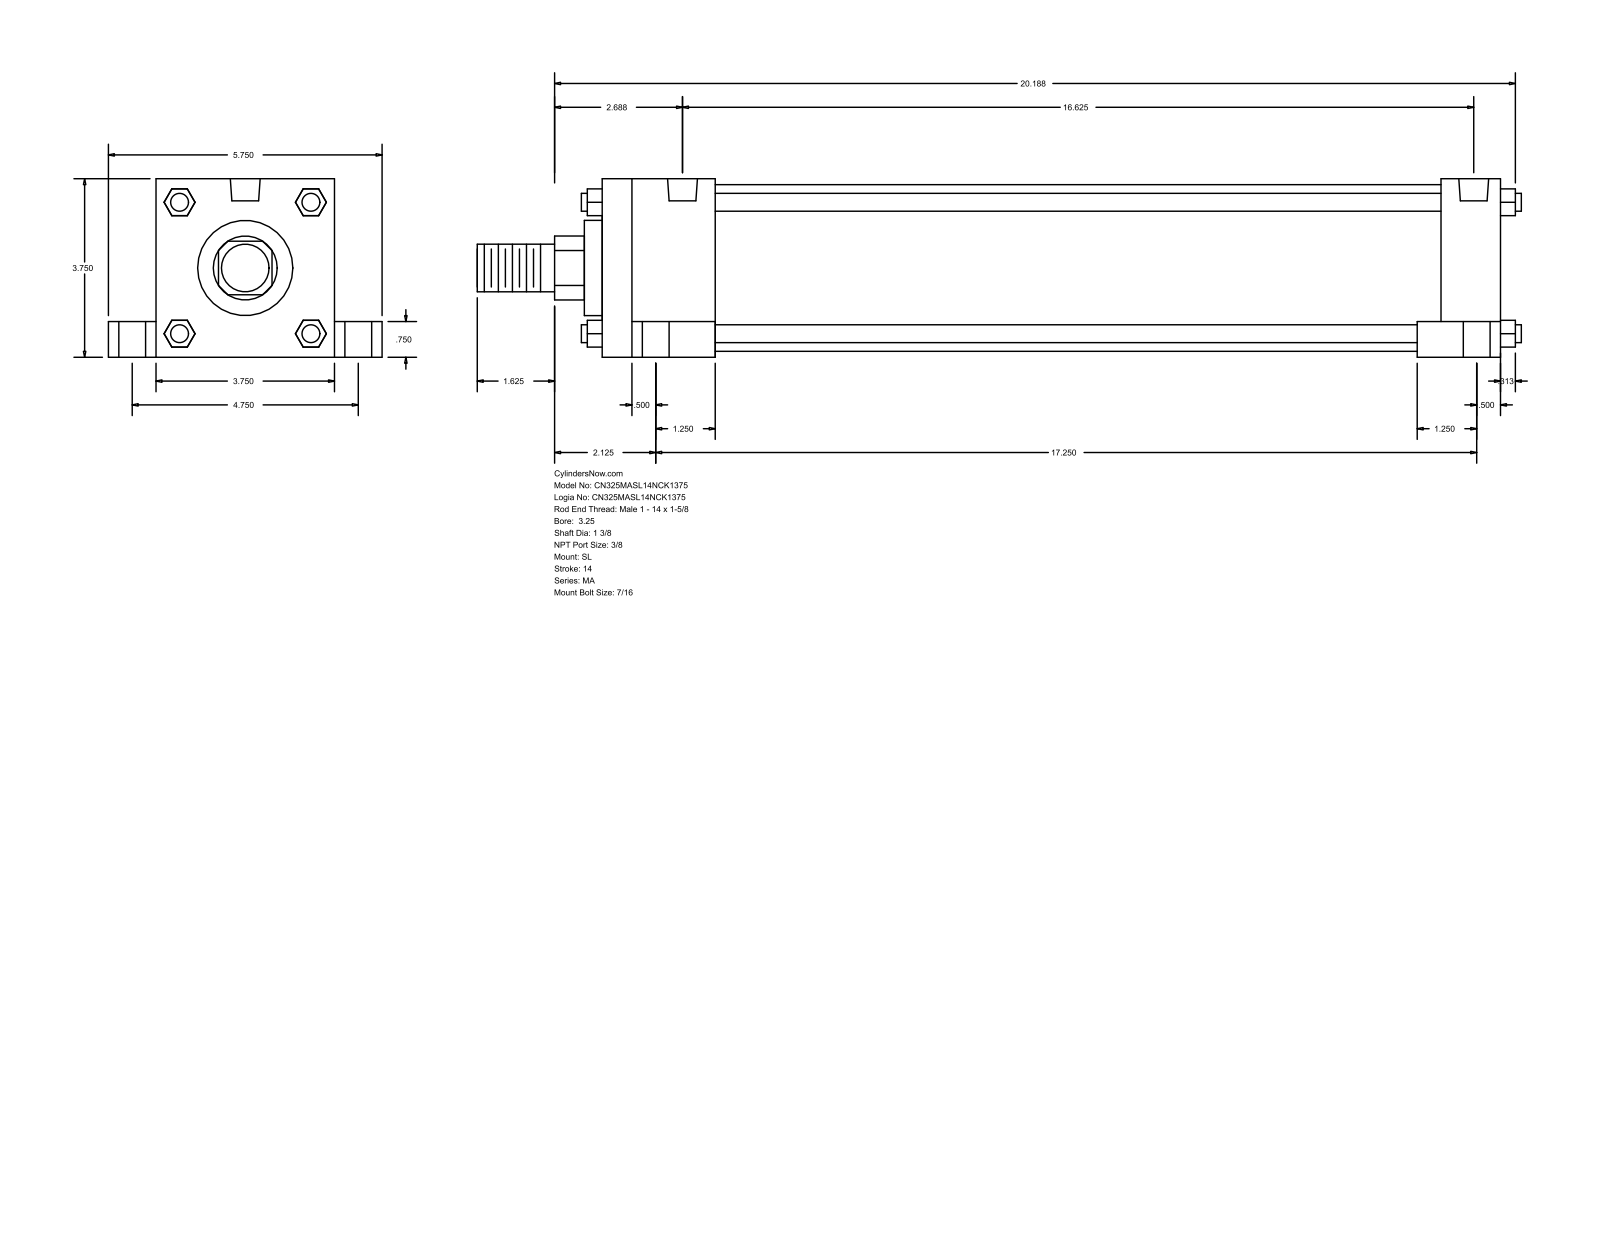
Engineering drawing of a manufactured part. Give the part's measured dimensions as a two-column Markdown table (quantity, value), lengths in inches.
| quantity | value |
| --- | --- |
| part name | MA_SL__0325_1.375 |
| STEP written by | GSSL Pune (CONFIG_CONTROL_DESIGN) |
| units | inches |
| bodies | 0 solids, 148 faces (112 planar, 36 cylindrical, 0 other) |
| overall size | 21.937 × 5.75 × 3.75 |
| round holes (diameter × count) | 0.437 × 4, 0.563 × 4, 0.813 × 4, 0.627 × 2 |
| round bosses / shafts (diameter × count) | 0.375 × 4, 3.5 × 1, 2 × 1, 1.375 × 1, 1 × 1 |
| partial cylindrical surfaces (radius × count) | 0.672 × 1 |
| main face-to-face distances | 3.75, 18.875, 15.25, 1, 4.75, 17.625, 1.25, 2.375, 16.5, 0.75 |
| hole center spacings | 0.188, 2.376, 2.388, 2.441, 2.491, 4.75, 16.25, 16.437 |
